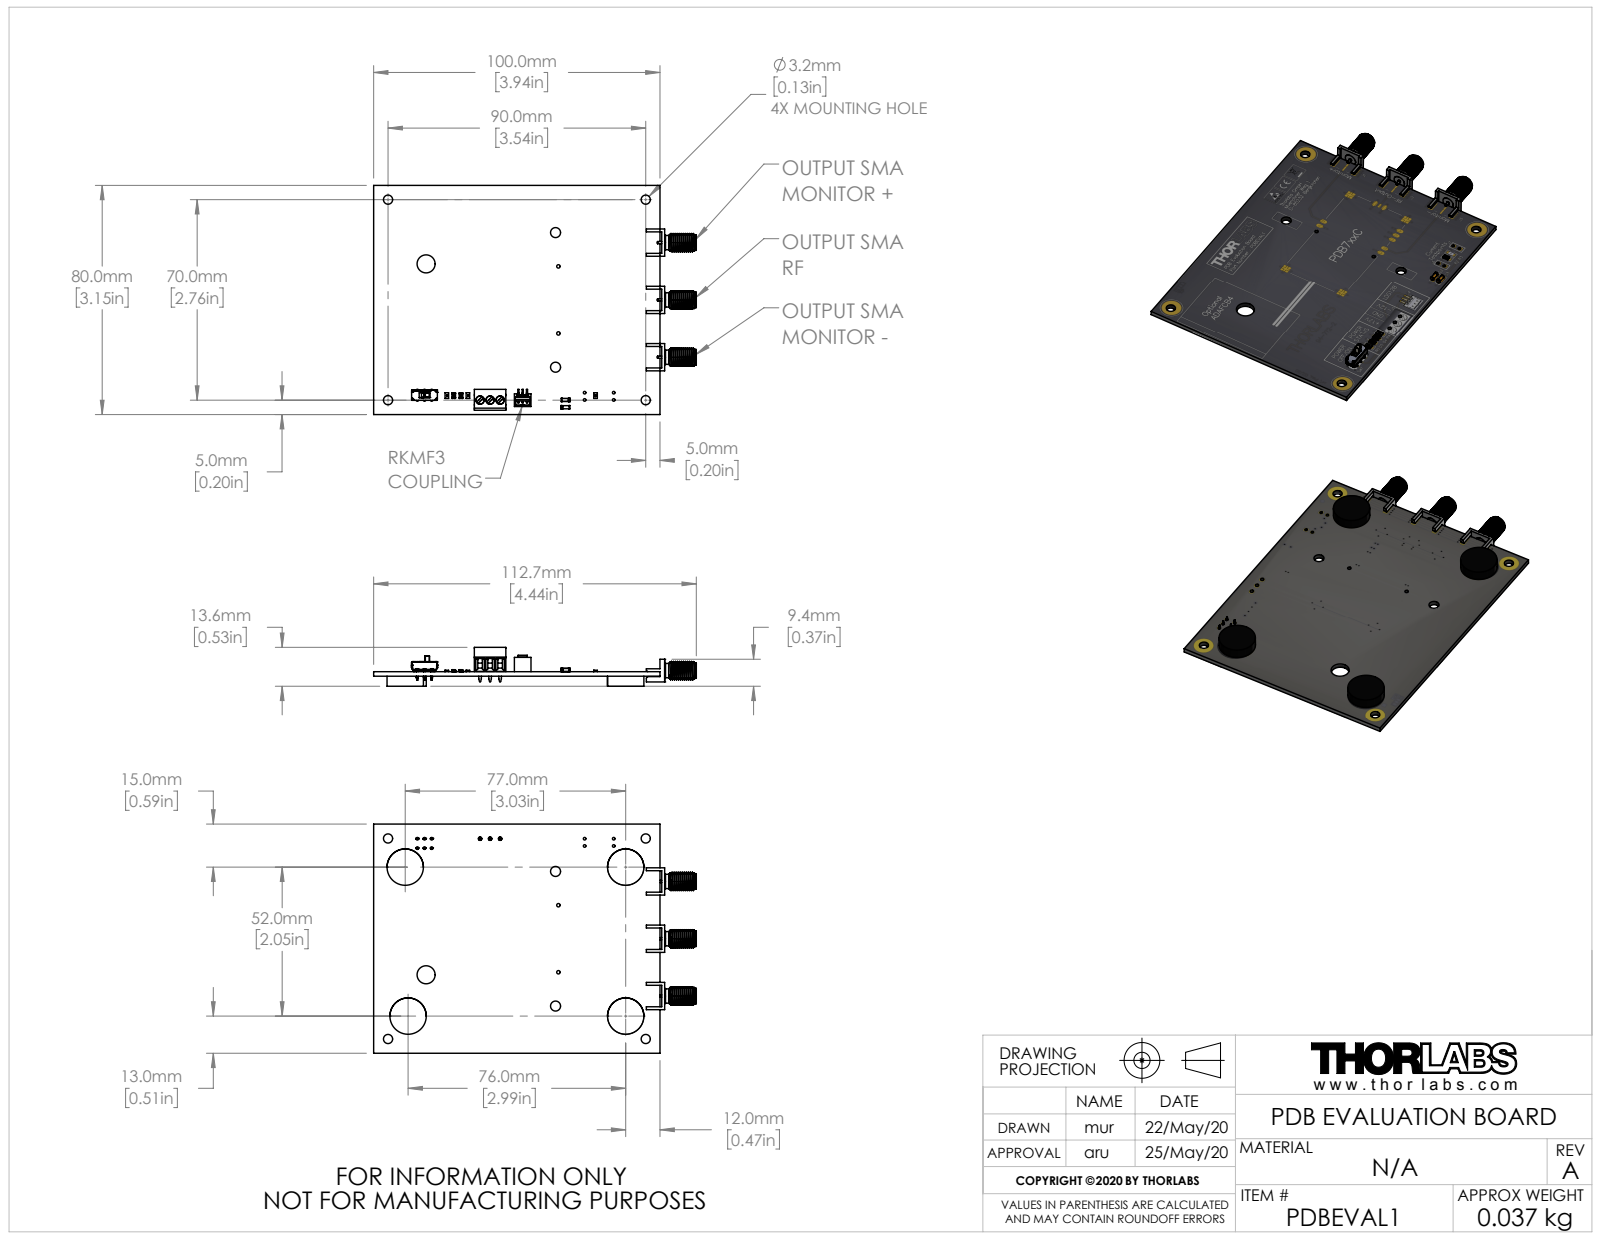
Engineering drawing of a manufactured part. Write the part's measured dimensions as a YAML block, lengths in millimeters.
part_name: "20.06.03_PDB EVAL_WEB"
step_written_by: "SolidWorks 2018 (AUTOMOTIVE_DESIGN)"
units: millimeters
bodies: {solids: 31, faces: 1284, planar: 944, cylindrical: 283, other: 57}
overall_size: [112.63, 79.95, 13.58]
volume: 16031
surface_area: 21414
round_holes:
  - {diameter: 0.9, count: 6}
  - {diameter: 1.2, count: 5}
  - {diameter: 0.91, count: 4}
  - {diameter: 3.2, count: 4}
  - {diameter: 0.84, count: 3}
  - {diameter: 2.9, count: 3}
  - {diameter: 4.28, count: 3}
  - {diameter: 4.6, count: 3}
  - {diameter: 3.5, count: 2}
  - {diameter: 6.3, count: 1}
round_bosses_or_shafts:
  - {diameter: 1.1, count: 5}
  - {diameter: 12.7, count: 4}
  - {diameter: 6.35, count: 3}
  - {diameter: 5.44, count: 3}
  - {diameter: 5, count: 3}
  - {diameter: 2.8, count: 3}
  - {diameter: 1, count: 3}
  - {diameter: 0.76, count: 3}
partial_cylinders:
  - {radius: 0.1, count: 18}
  - {radius: 0.16, count: 10}
  - {radius: 0.5, count: 9}
  - {radius: 0.2, count: 6}
  - {radius: 0.15, count: 4}
  - {radius: 0.21, count: 4}
  - {radius: 0.25, count: 4}
  - {radius: 0.3, count: 4}
face_to_face_distances: [1.58, 3.5, 5.08, 1.01, 20, 79.94, 100.57, 101.58, 99.94, 0.63]
hole_center_spacings: [3.5, 2.5, 4.14, 7, 3.3, 2.54, 5, 5.99]
